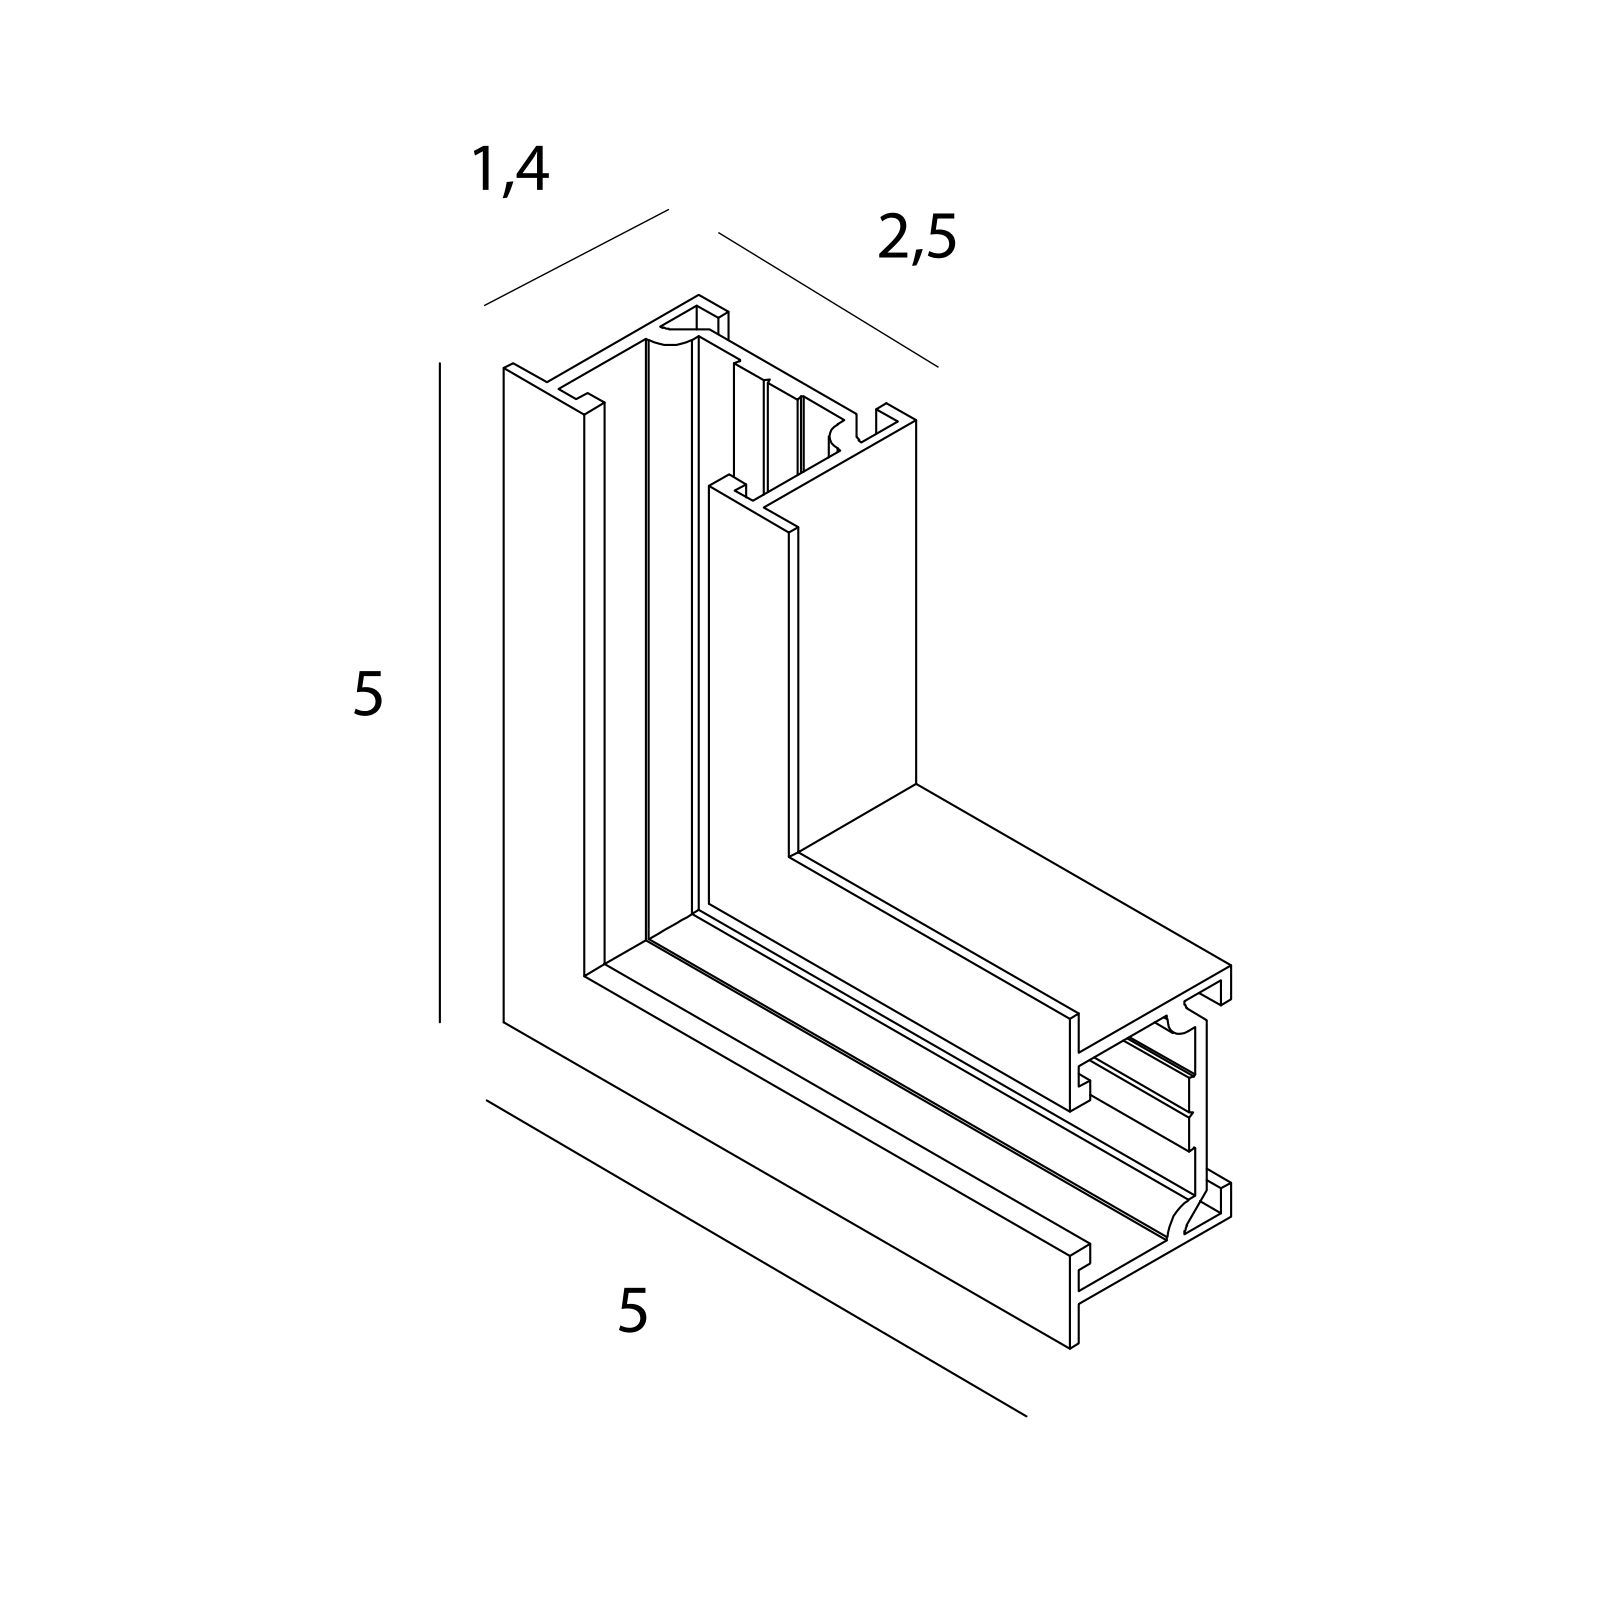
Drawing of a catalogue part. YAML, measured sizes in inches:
part_name: "NT0013 v3"
step_written_by: "Autodesk Translation Framework v14.24.0.0 (AUTOMOTIVE_DESIGN)"
units: inches
bodies: {solids: 1, faces: 79, planar: 67, cylindrical: 12, other: 0}
overall_size: [1.969, 1.969, 0.56]
volume: 0.306
surface_area: 15.82
partial_cylinders:
  - {radius: 0.004, count: 4}
  - {radius: 0.02, count: 4}
  - {radius: 0.075, count: 4}
face_to_face_distances: [0.039, 0.716, 0.475, 0.404, 0.755, 0.444, 0.031, 0.436, 0.124, 0.085]
